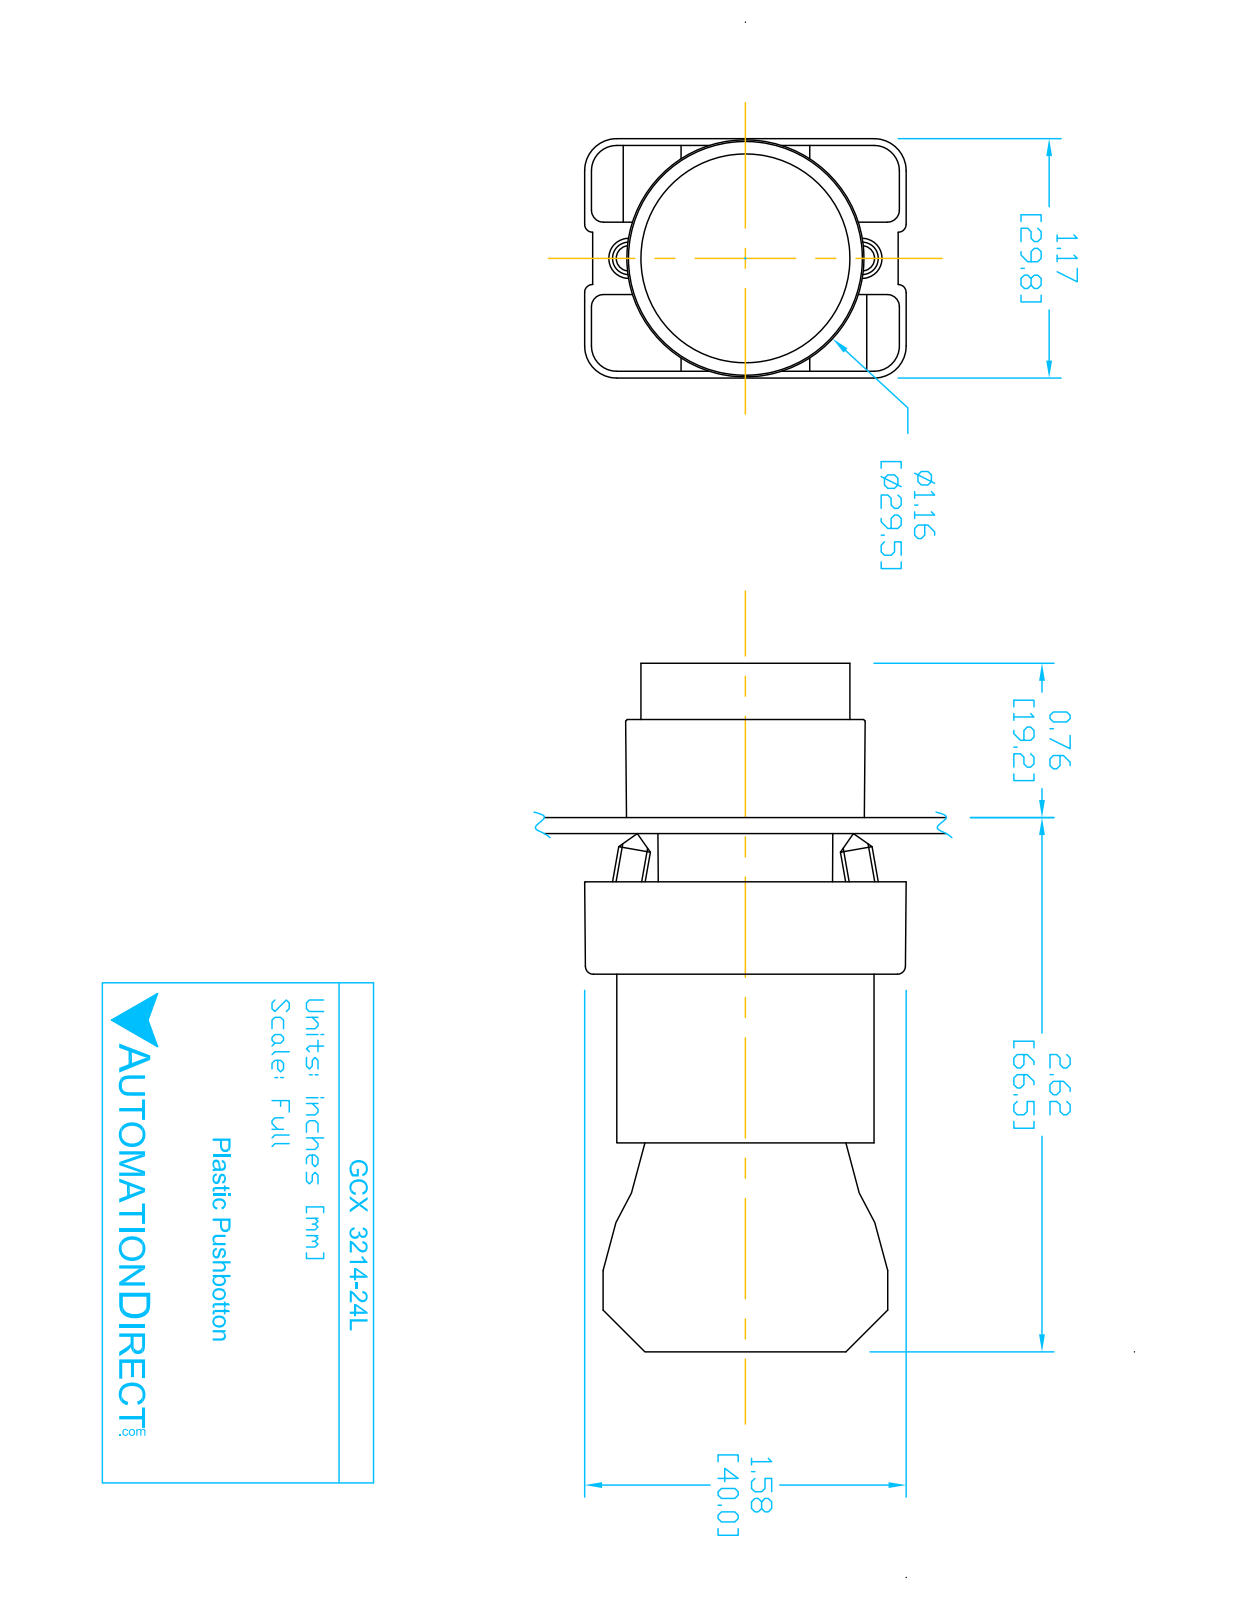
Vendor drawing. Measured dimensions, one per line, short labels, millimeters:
name: ecx1040; GCX3214L OPERATOR; GCX3214-24L; ECX3029-2 (+1 more)
written by: SolidWorks 2016 (AUTOMOTIVE_DESIGN)
unit: mm
bodies: 7 solids, 425 faces (250 planar, 144 cylindrical, 31 other)
size: 84.3 × 40.2 × 29.9
volume: 44 590 mm³; area: 23 430 mm²
holes: 2× ⌀2, 2× ⌀3.1, 2× ⌀3.3, 1× ⌀2.2, 1× ⌀5, 1× ⌀11.9, 1× ⌀22.3, 1× ⌀22.6, 1× ⌀26
bosses: 4× ⌀4, 1× ⌀29.8, 1× ⌀25.5, 1× ⌀24, 1× ⌀21.7, 1× ⌀19.8, 1× ⌀12.8
rounds: 24× R1.5, 12× R1, 12× R3.1, 12× R4, 8× R1, 2× R3.3, 1× R0.5, 1× R1.6
face distances: 21, 14.7, 29.7, 51.3, 30.3, 0.8, 0.8, 14.6, 29.6, 15.1
hole spacings: 6, 13.8, 12, 12.4
